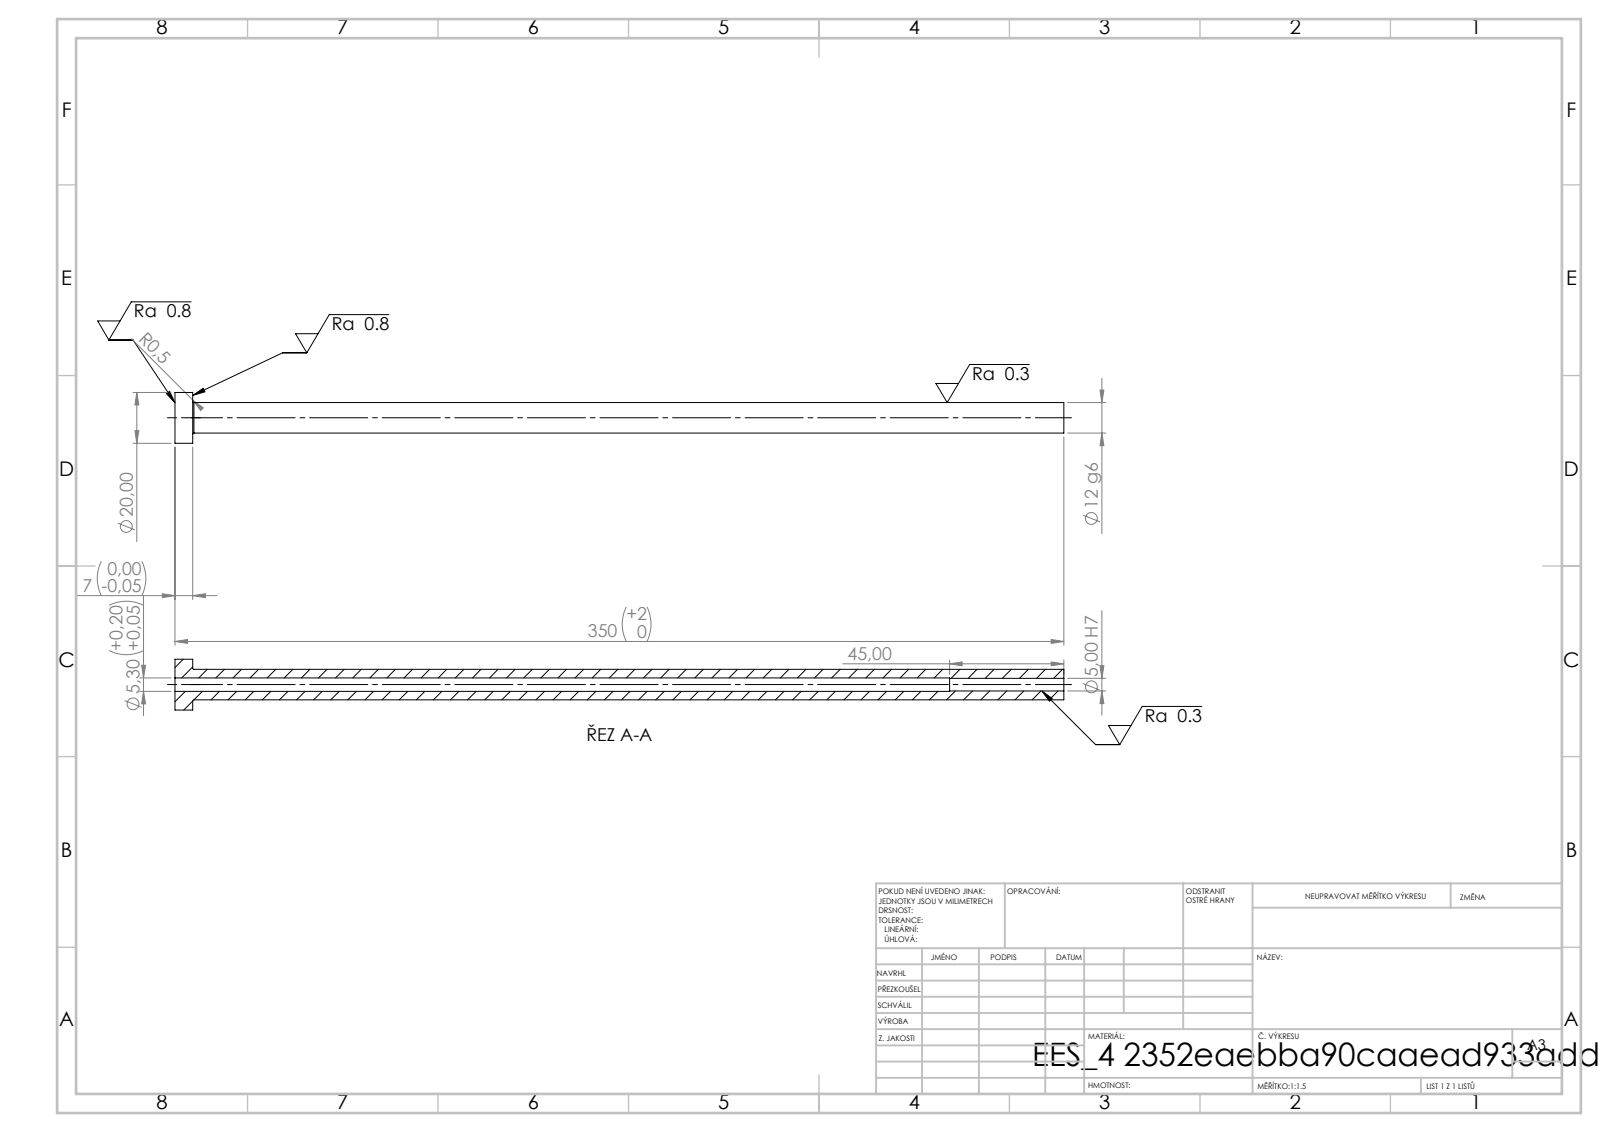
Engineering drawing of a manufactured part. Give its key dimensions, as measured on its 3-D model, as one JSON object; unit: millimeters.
{"step_written_by": "SolidWorks 2019 (CONFIG_CONTROL_DESIGN)", "units": "millimeters", "bodies": {"solids": 1, "faces": 14, "planar": 4, "cylindrical": 8, "other": 2}, "overall_size": [350, 20, 20], "volume_mm3": 33381, "surface_area_mm2": 19737, "round_holes": [[5, 1], [5.3, 1]], "round_bosses_or_shafts": [[20, 1], [12, 1]], "face_to_face_distances": [7, 350, 343, 305, 298, 45]}
